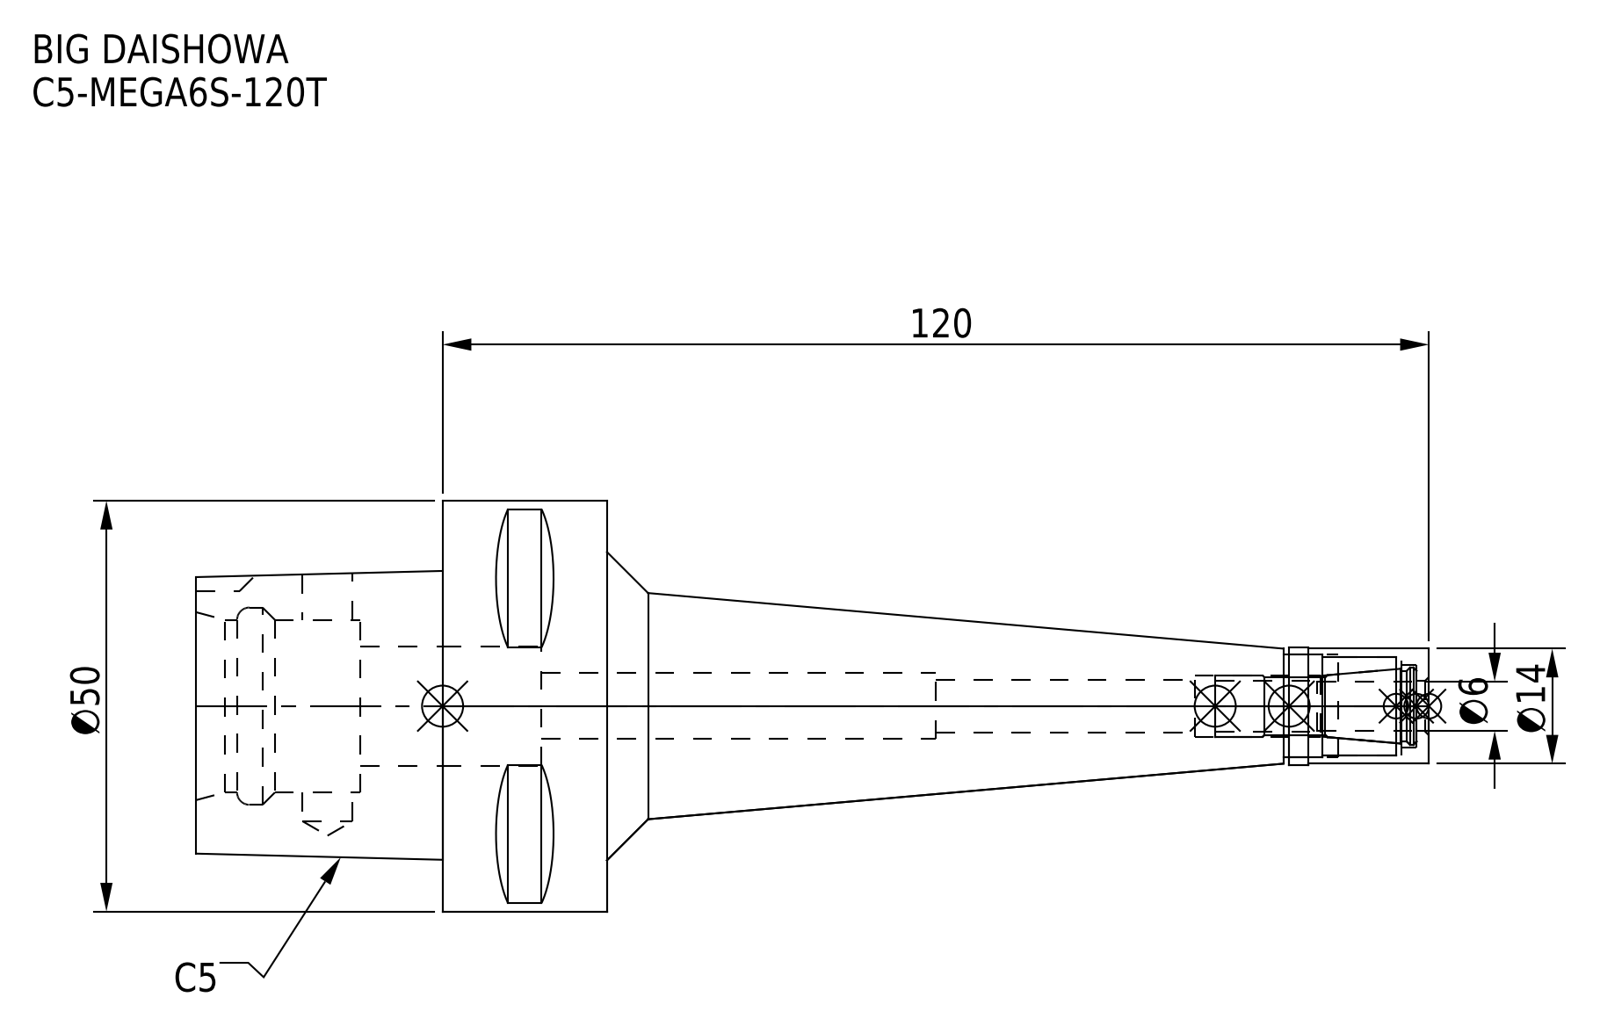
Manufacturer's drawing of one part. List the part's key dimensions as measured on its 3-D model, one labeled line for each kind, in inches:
Part name (STEP PRODUCT): C5-MEGA6S-120T-060.stp; C5-MEGA6S-120T-060_ASM.stp; DXF_TEMP_ASSY_ASM_4_ASM.stp; C5-MEGA6S-120T (+3 more)
STEP written by: SolidWorks 2019 (CONFIG_CONTROL_DESIGN)
Units: inches
Bodies: 2 solids, 93 faces (38 planar, 37 cylindrical, 18 other)
Overall size (bounding box): 5.906 × 1.969 × 1.969
Volume: 5.104 in³ · Surface area: 34.56 in²
Round holes (diameter × count): ⌀0.24 ×2, ⌀0.252 ×1, ⌀0.291 ×1, ⌀0.315 ×1, ⌀0.394 ×1, ⌀0.472 ×1, ⌀0.492 ×1, ⌀0.571 ×1, ⌀0.827 ×1, ⌀0.945 ×1
Round bosses / shafts (diameter × count): ⌀1.969 ×1, ⌀0.563 ×1, ⌀0.551 ×1
Partial cylindrical surfaces — rounded edges, fillets, slot ends (radius × count): R0.157 ×1
Main face-to-face distances: 0.787, 1.181, 1.969, 1.732, 0.394, 0.755, 0.313, 0.474, 5.118, 0.315
